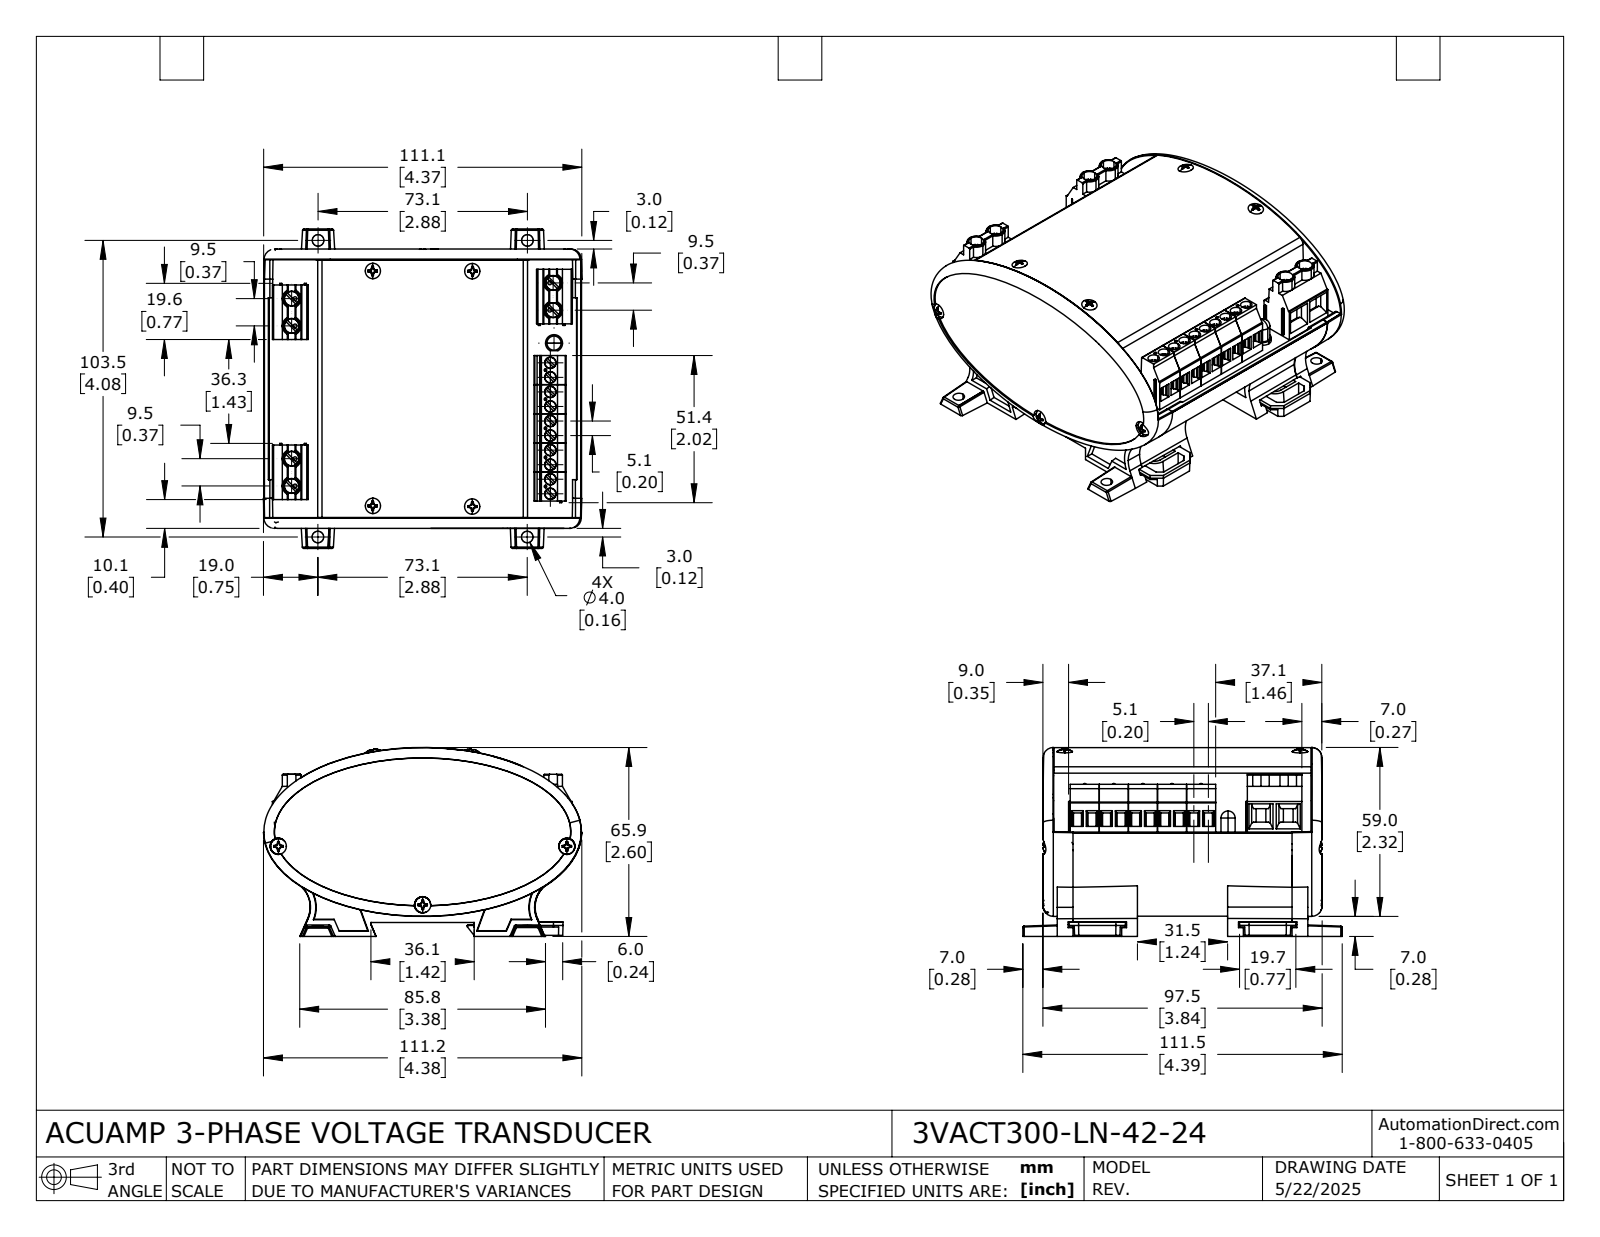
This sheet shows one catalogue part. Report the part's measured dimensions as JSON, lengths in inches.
{"part_name": "3VACT300-LN-42-24", "step_written_by": "SolidWorks 2024 (AUTOMOTIVE_DESIGN)", "units": "inches", "bodies": {"solids": 26, "faces": 2965, "planar": 1484, "cylindrical": 838, "other": 643}, "overall_size": [4.391, 4.377, 2.597], "volume_in3": 8.539, "surface_area_in2": 197.4, "round_holes": [[0.05, 12], [0.157, 10], [0.08, 6], [0.111, 6], [0.205, 6], [0.126, 4]], "round_bosses_or_shafts": [[0.051, 16], [0.15, 10], [0.112, 10], [0.067, 10], [0.197, 6], [0.018, 4], [0.234, 1], [0.194, 1]], "partial_cylinders_radius": [[0.006, 40], [0.039, 20], [0.008, 16], [0.02, 16], [0.01, 6], [0.012, 6], [0.128, 6], [0.018, 4]], "face_to_face_distances": [0.063, 0.128, 3.672, 3.8, 3.543, 0.084, 0.394, 3.406, 0.266, 3.278], "hole_center_spacings": [0.2, 0.4, 0.6, 0.8, 1, 1.2, 1.4, 1.6]}
